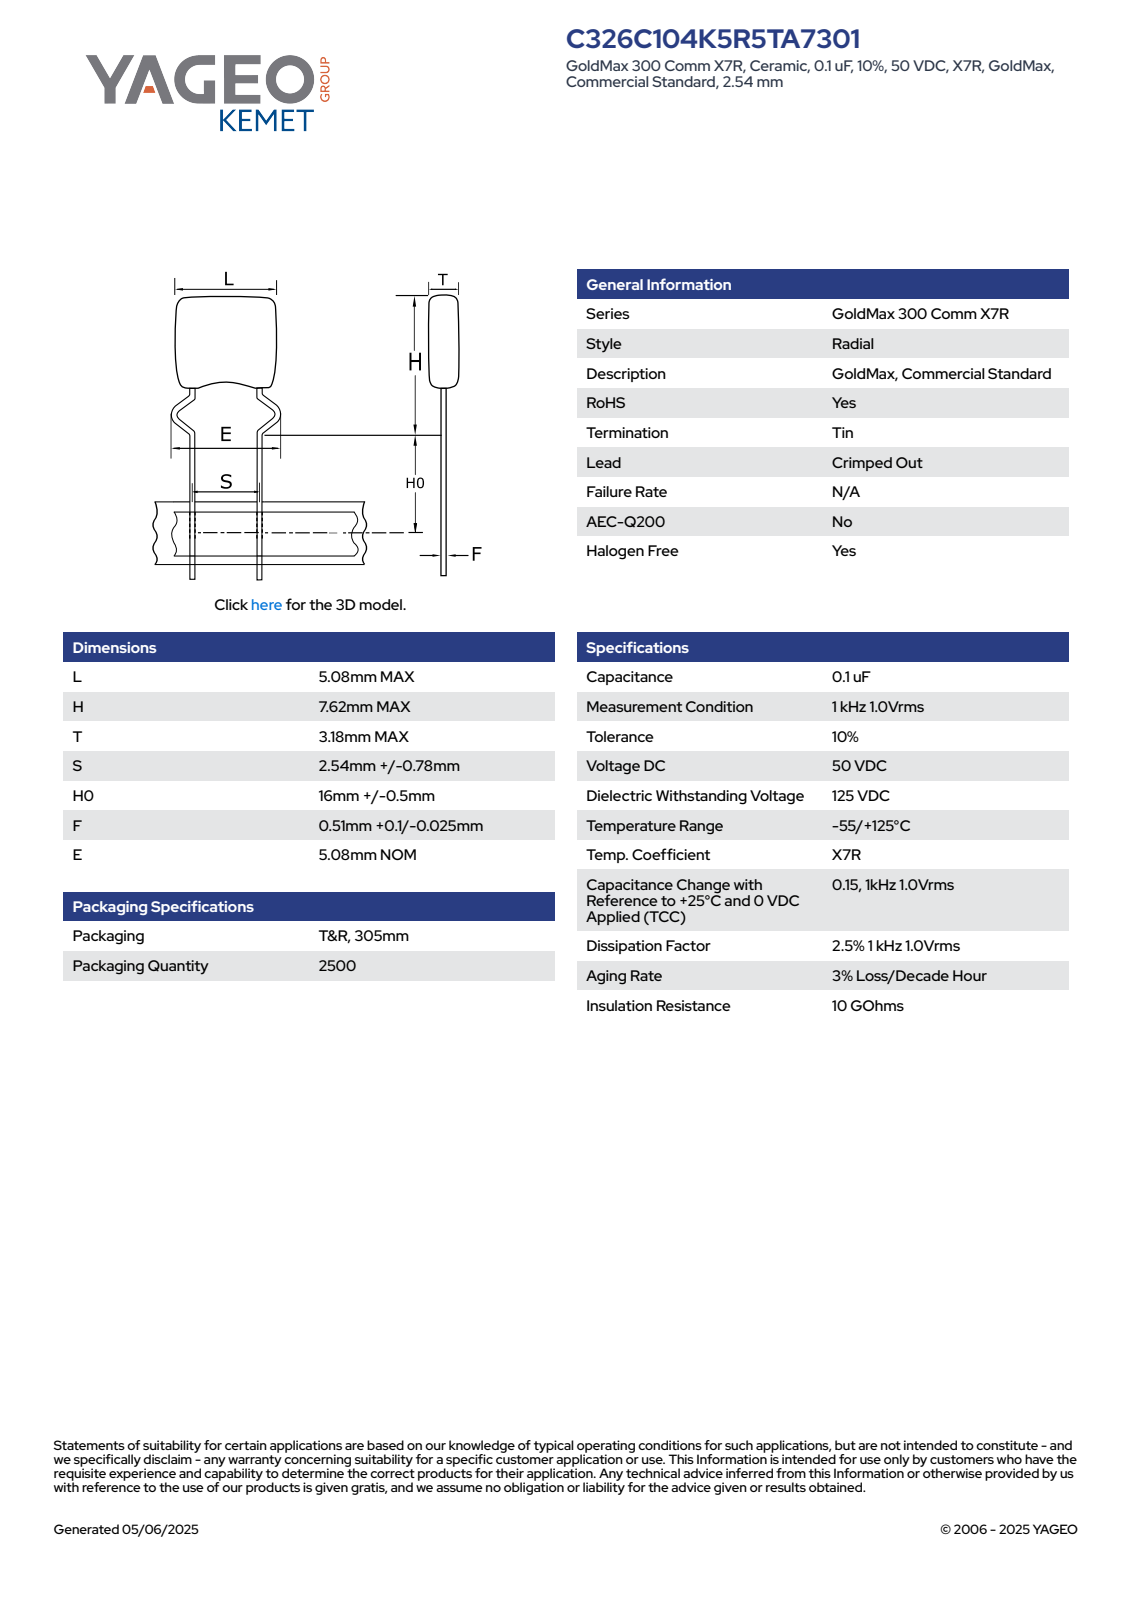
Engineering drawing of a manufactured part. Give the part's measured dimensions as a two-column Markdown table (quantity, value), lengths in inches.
| quantity | value |
| --- | --- |
| part name | CCR_RCCRTAPE_C326_L5.08H7.62T3.18S2.54H016.5F0.51E5.08 |
| STEP written by | SolidWorks 2014 (AUTOMOTIVE_DESIGN) |
| units | inches |
| bodies | 4 solids, 104 faces (66 planar, 16 cylindrical, 22 other) |
| overall size | 0.95 × 0.2 × 0.126 |
| volume | 0.005 in³ |
| surface area | 0.26 in² |
| round bosses / shafts (diameter × count) | 0.02 × 2 |
| partial cylindrical surfaces (radius × count) | 0.01 × 8, 0.03 × 4 |
| main face-to-face distances | 0.125, 0.2, 0.189, 0.126, 0.761, 0.95, 0.08, 0.032, 0.869, 0.109 |
